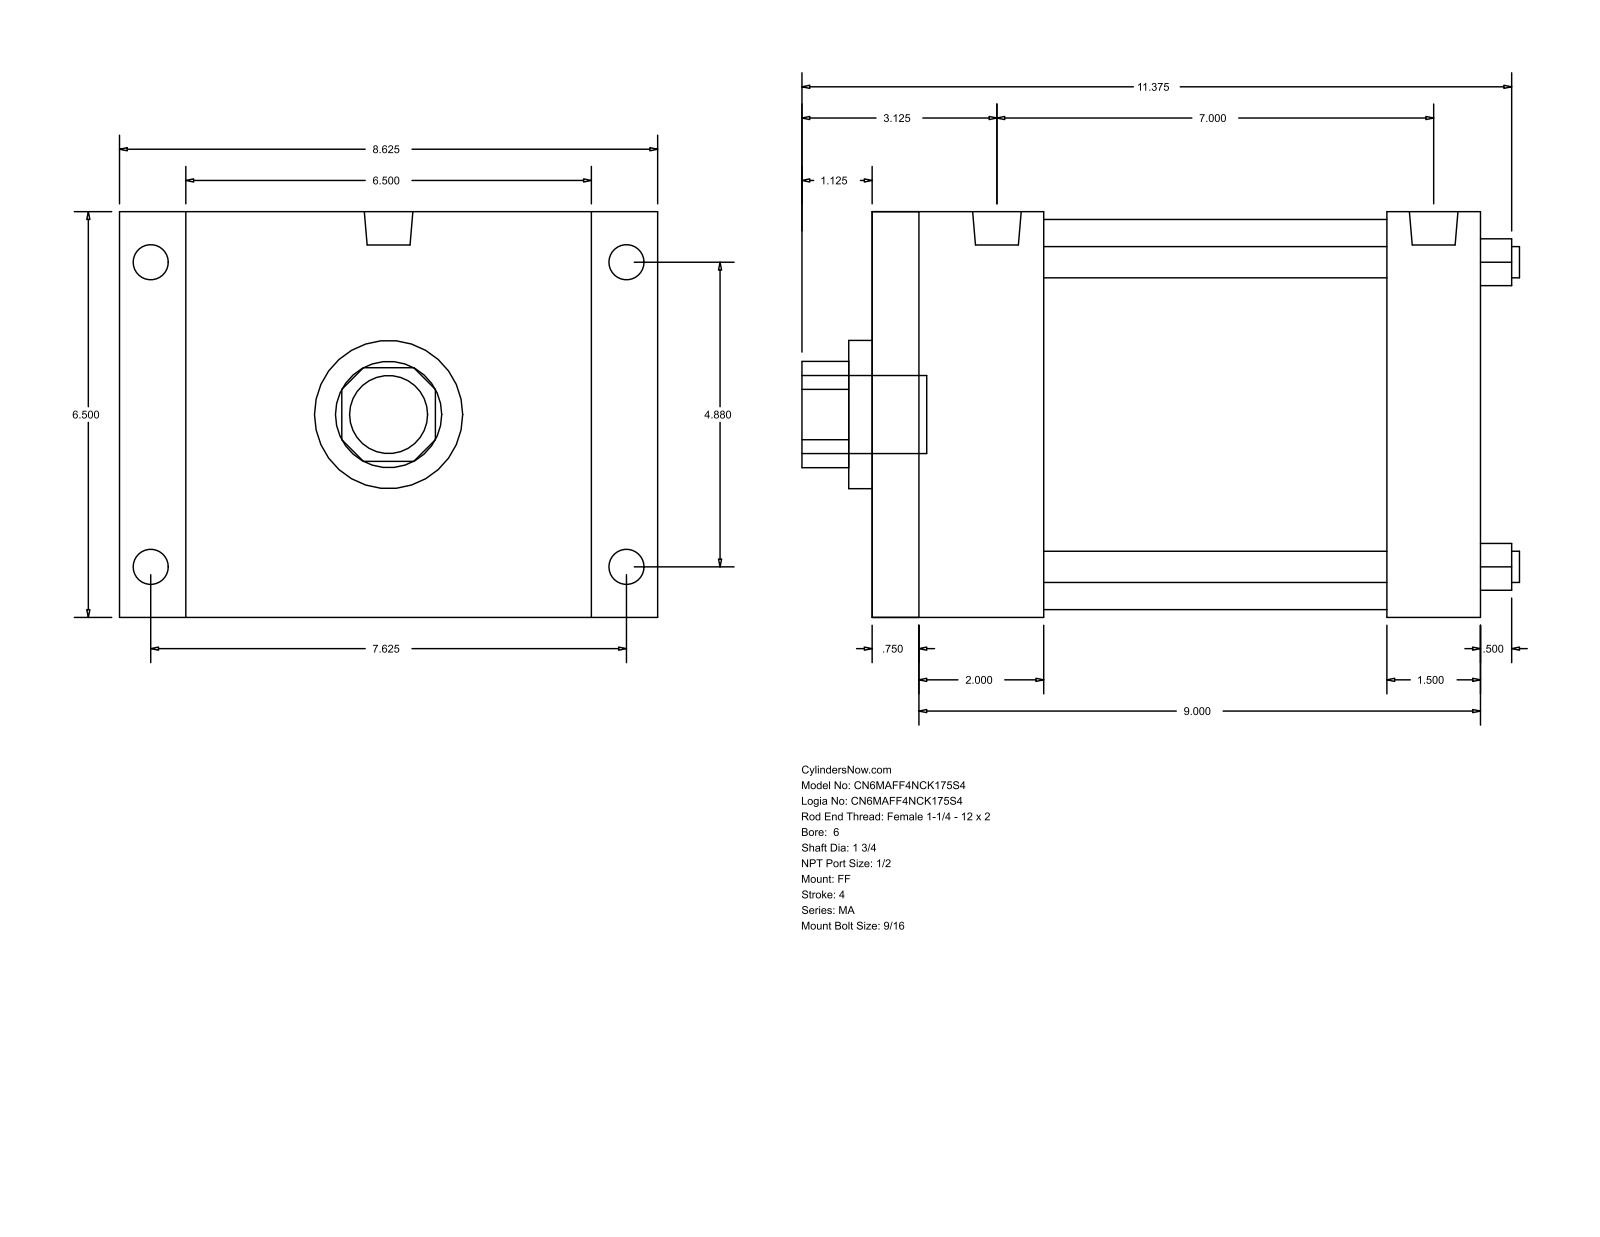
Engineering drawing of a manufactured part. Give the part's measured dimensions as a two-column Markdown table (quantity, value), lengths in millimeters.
| quantity | value |
| --- | --- |
| part name | MA_FF__0600_1.75 |
| STEP written by | GSSL Pune (CONFIG_CONTROL_DESIGN) |
| units | millimeters |
| bodies | 0 solids, 92 faces (64 planar, 28 cylindrical, 0 other) |
| overall size | 292.1 × 219.07 × 165.1 |
| round holes (diameter × count) | 12.7 × 4, 44.45 × 1, 60.33 × 1, 158.75 × 1 |
| round bosses / shafts (diameter × count) | 17.46 × 4, 14.29 × 4, 19.77 × 2, 31.75 × 1 |
| partial cylindrical surfaces (radius × count) | 21.63 × 1 |
| main face-to-face distances | 165.1, 247.66, 19.05, 228.61, 50.8, 69.85, 177.81, 209.55, 190.5, 139.7 |
| hole center spacings | 87.65, 123.96, 175.31 |
